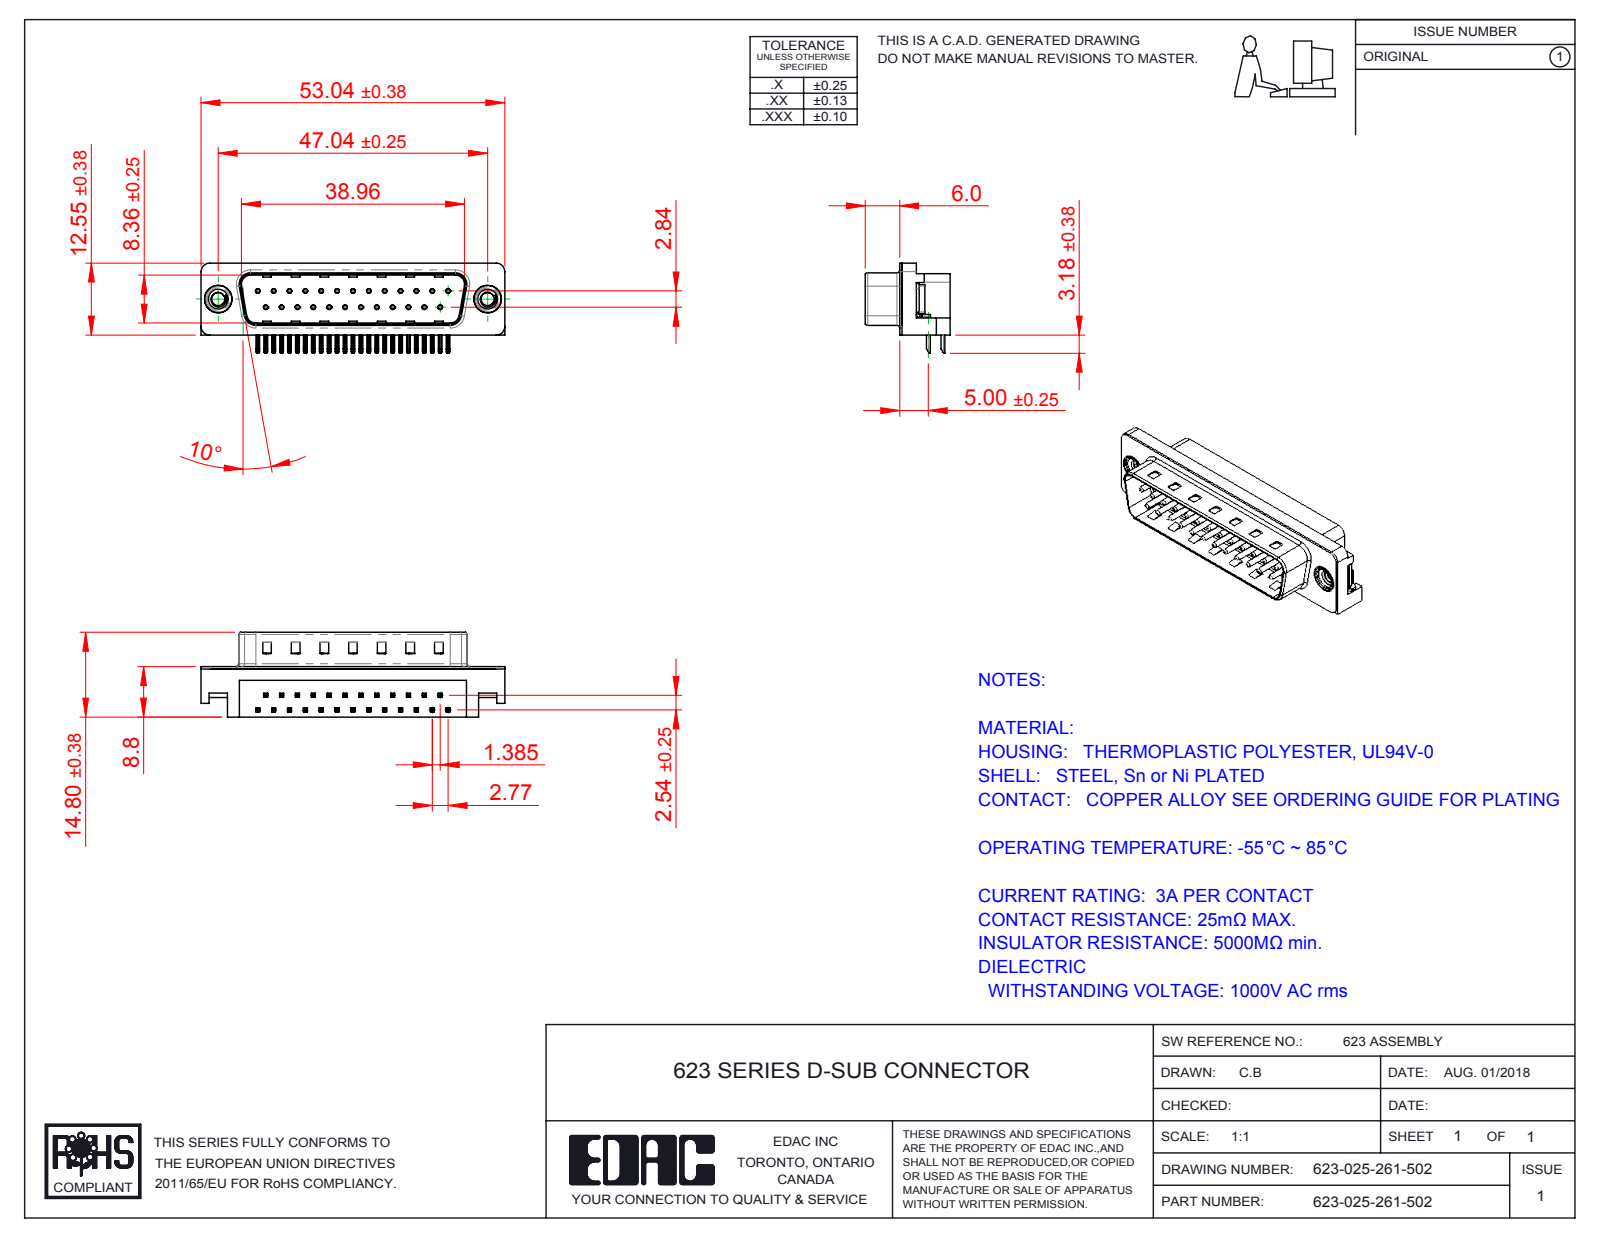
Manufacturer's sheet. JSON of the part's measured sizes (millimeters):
{"part_name": "623 Contact Bottom; 623 Shell_25 Socket; 623 Contact Top; 623-025-261-502 (+3 more)", "step_written_by": "SolidWorks 2016 (CONFIG_CONTROL_DESIGN)", "units": "millimeters", "bodies": {"solids": 31, "faces": 2253, "planar": 1405, "cylindrical": 649, "other": 199}, "overall_size": [53.04, 15.73, 14.8], "volume_mm3": 4726, "surface_area_mm2": 6717, "round_holes": [[0.35, 25], [0.8, 25], [2.26, 2], [4, 2], [4.8, 2], [5, 2]], "round_bosses_or_shafts": [[0.75, 25], [4.9, 2], [4.75, 2], [3.9, 2]], "partial_cylinders_radius": [[0.25, 108], [0.12, 50], [1, 16], [0.5, 9], [1.5, 7], [0.9, 4], [1.6, 4], [2, 4]], "face_to_face_distances": [0.4, 8.4, 2.1, 1.7, 8.76, 10.46, 10.86, 10.35, 8.8, 5.9], "hole_center_spacings": [3.16, 2.77, 11.08, 5.54, 8.31, 5.03, 13.85, 7.48]}
